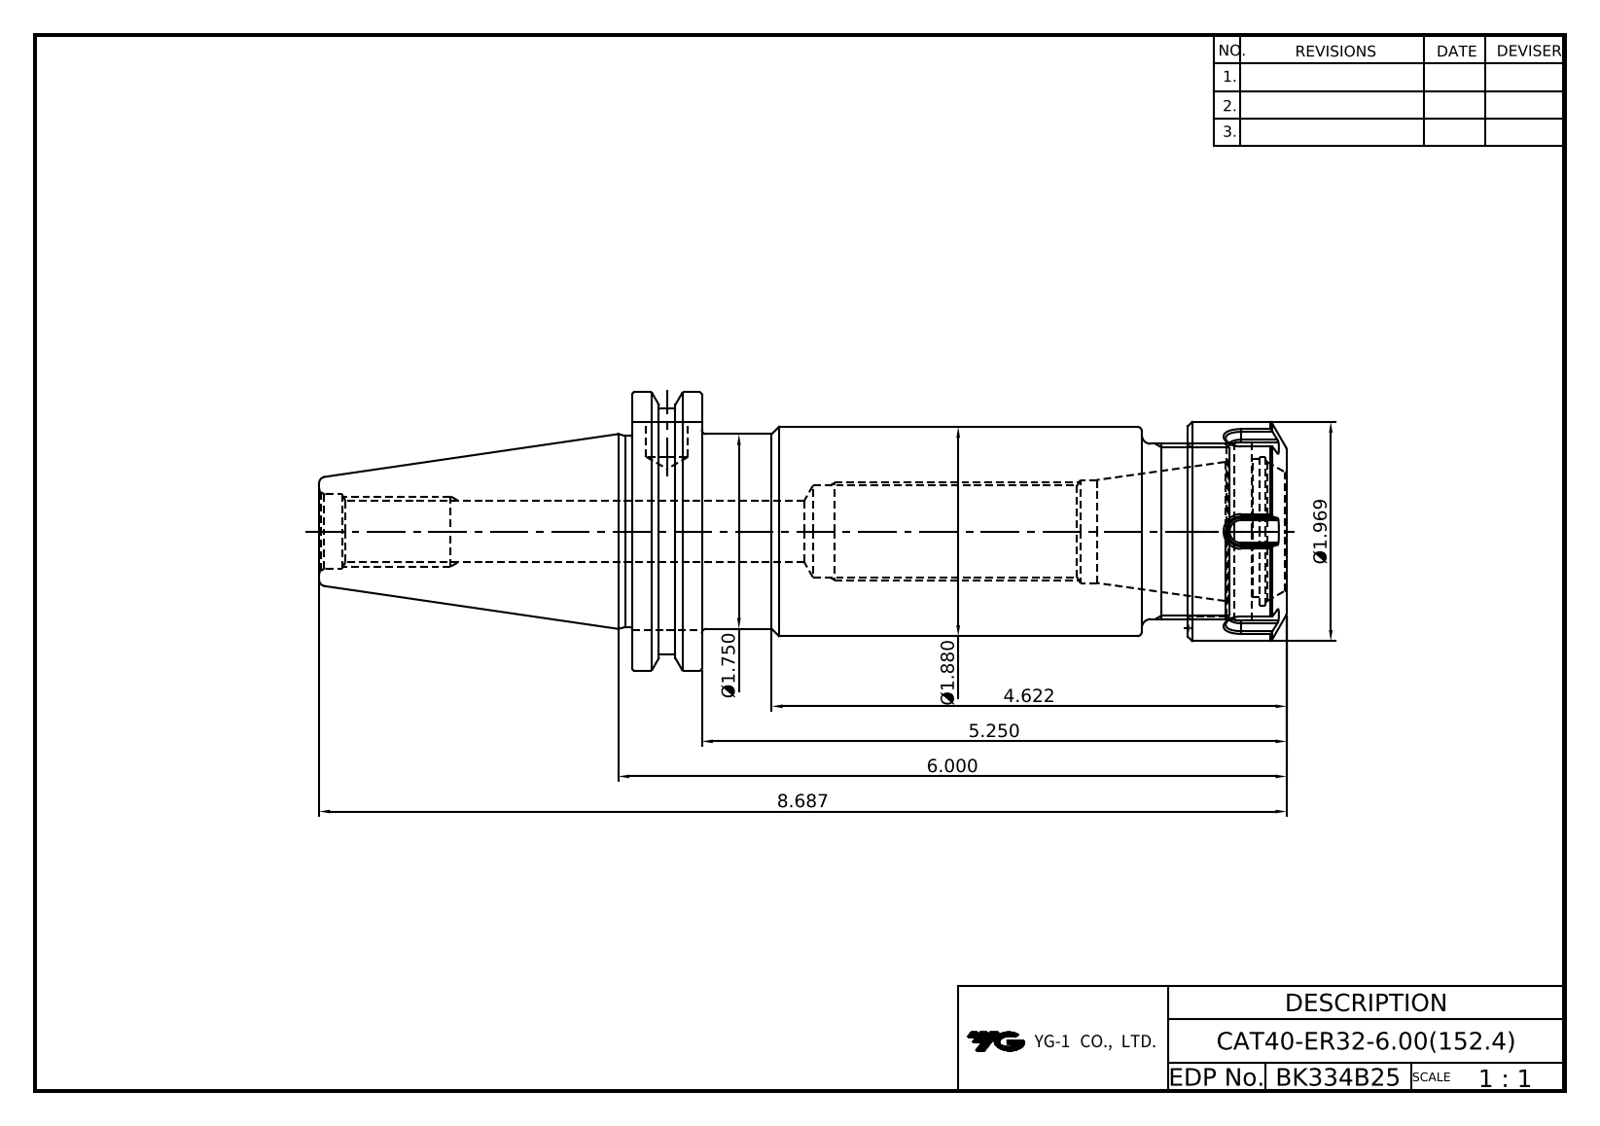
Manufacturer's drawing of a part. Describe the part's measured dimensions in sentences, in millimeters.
The part is named "LO-CAT40-ER32-152.4; ER32NUT". Its 3-D file was written by "Autodesk Inventor 2025 (AUTOMOTIVE_DESIGN)". It is 2 solids with 143 faces: 64 planar, 33 cylindrical and 46 other. Overall it measures 220.65 by 63.5 by 61.09 millimeters. Its volume is 230 300 cubic millimeters and its surface area 51 781 square millimeters. Round holes: 1 of diameter 1, 1 of diameter 9.53, 1 of diameter 13.39, 1 of diameter 16.3, 1 of diameter 20.5, 1 of diameter 23.5, 1 of diameter 27.1, 1 of diameter 31.4, 1 of diameter 33.8, 1 of diameter 38.6, 1 of diameter 40.5. Round bosses or shafts: 1 of diameter 63.5, 1 of diameter 56.3, 1 of diameter 50, 1 of diameter 44.45, 1 of diameter 43.6, 1 of diameter 40. Partial cylindrical surfaces (rounded edges, fillets, slot ends): 12 of radius 0.5. The main face-to-face distances are 15.88, 149.23, 133.35, 126.73, 110.85, 22.5, 141.33, 125.45, 14.6, 7.9. The hole center spacings are 0.8, 22, 22.8.
